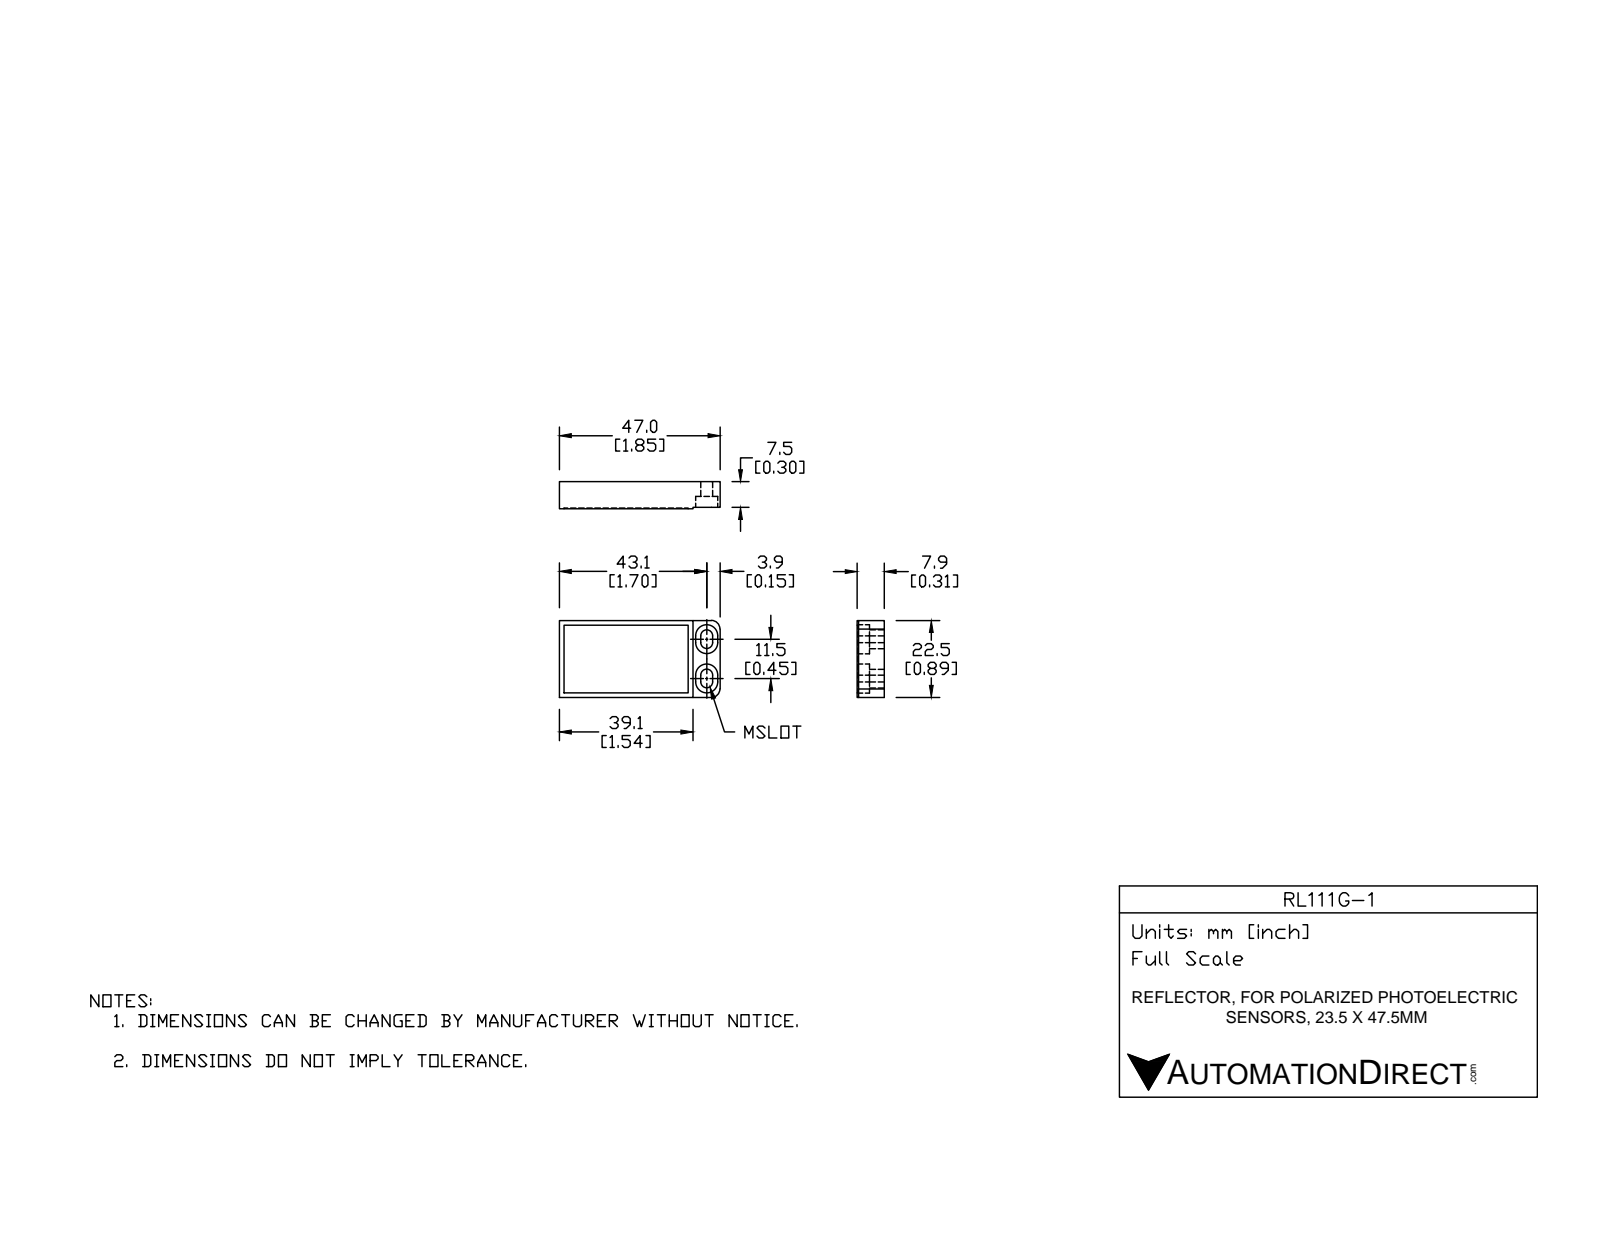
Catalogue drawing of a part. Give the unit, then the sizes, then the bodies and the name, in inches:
Units: inches
Overall size (bounding box): 1.85 × 0.886 × 0.311
Partial cylindrical surfaces — rounded edges, fillets, slot ends (radius × count): R0.069 ×4, R0.128 ×4, R0.098 ×2
Main face-to-face distances: 0.303, 0.886, 0.311, 1.85, 0.295, 0.016, 0.169, 0.126, 0.134, 0.142
Volume: 0.469 in³ · Surface area: 5.311 in²
Bodies: 1 solid, 33 faces (23 planar, 10 cylindrical, 0 other)
Part name (STEP PRODUCT): RL-111G-1
STEP written by: SolidWorks 2017 (AUTOMOTIVE_DESIGN)
